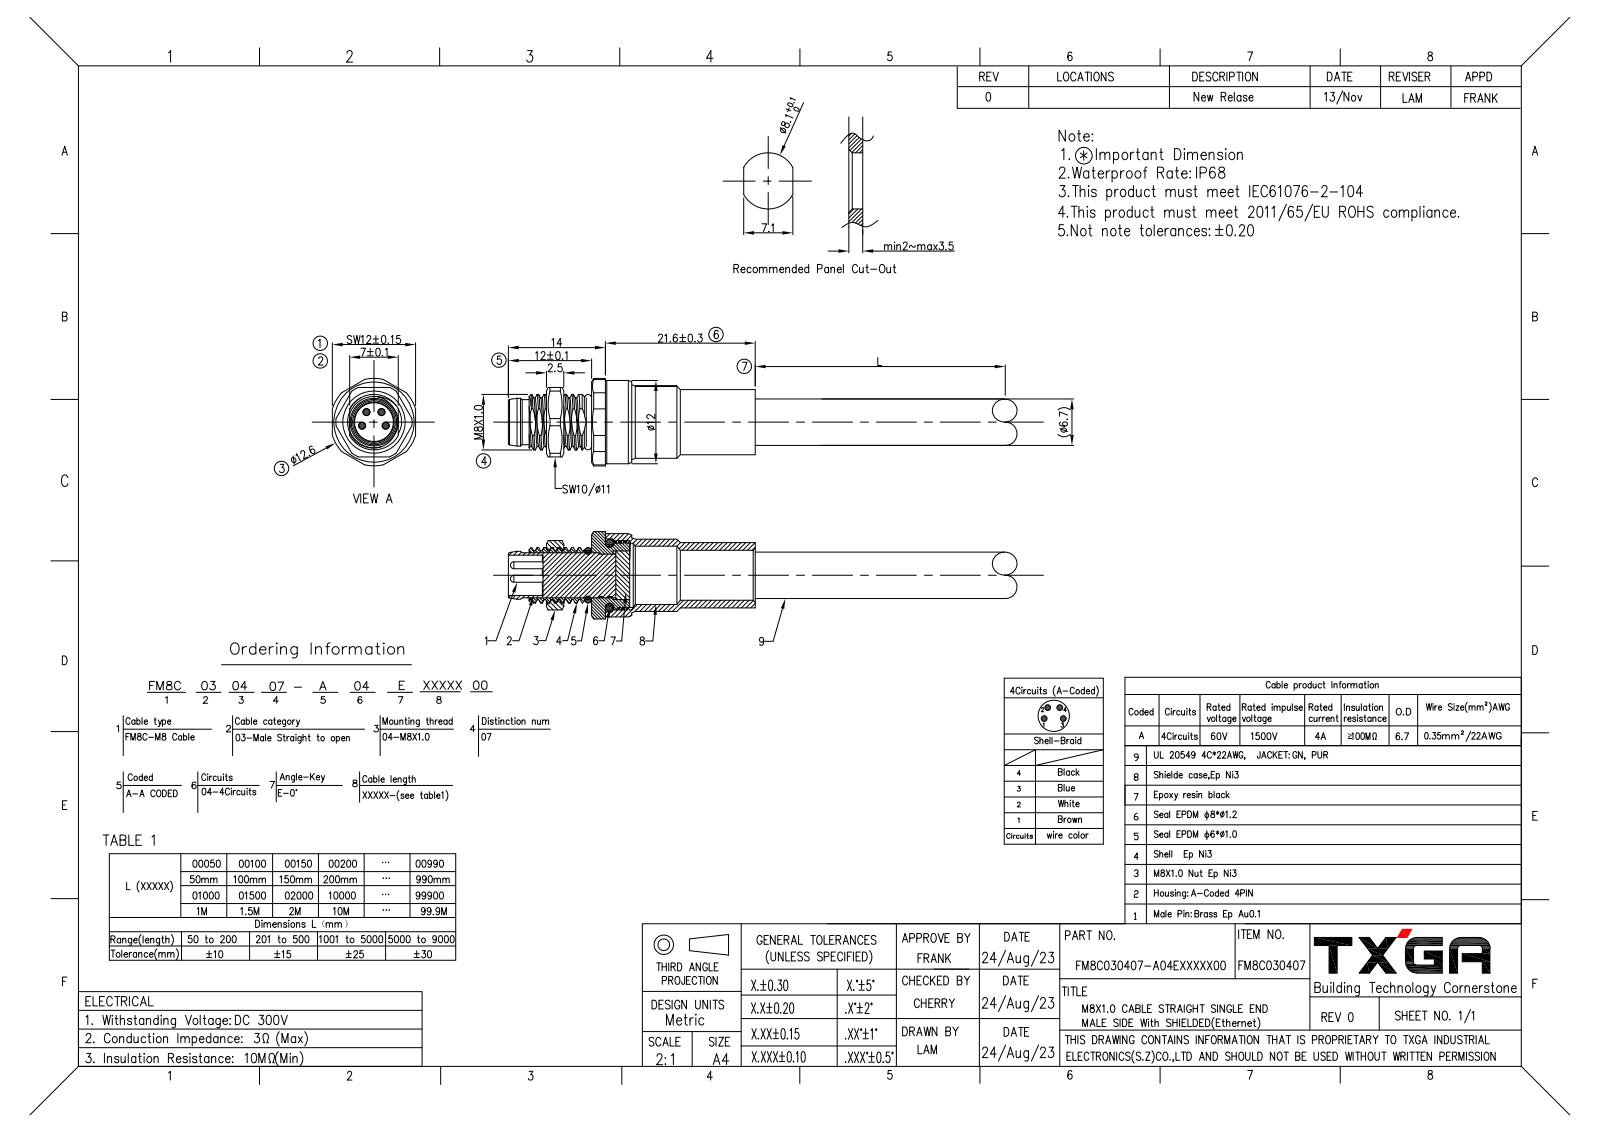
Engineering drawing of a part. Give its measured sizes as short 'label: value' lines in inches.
name: PRT000122344
written by: PRO/ENGINEER BY PARAMETRIC TECHNOLOGY CORPORATION, 2010280 (CONFIG_CONTROL_DESIGN)
unit: in
bodies: 1 solid, 388 faces (99 planar, 167 cylindrical, 122 other)
size: 2.425 × 0.496 × 0.472
volume: 0.023 in³; area: 7.299 in²
holes: 4× ⌀0.033, 4× ⌀0.041, 4× ⌀0.059, 2× ⌀0.031, 1× ⌀0.228, 1× ⌀0.276, 1× ⌀0.283, 1× ⌀0.331, 1× ⌀0.364, 1× ⌀0.413
bosses: 4× ⌀0.061, 4× ⌀0.057, 4× ⌀0.039, 1× ⌀0.472, 1× ⌀0.409, 1× ⌀0.394, 1× ⌀0.37, 1× ⌀0.346
rounds: 2× R0.03, 1× R0.12, 1× R0.217, 1× R0.248
face distances: 0.079, 0.138, 0.039, 0.098, 0.217, 0.394, 0.059, 0.433, 0.472, 0.28
hole spacings: 0.134, 0.07, 0.071, 0.081, 0.077, 0.085
